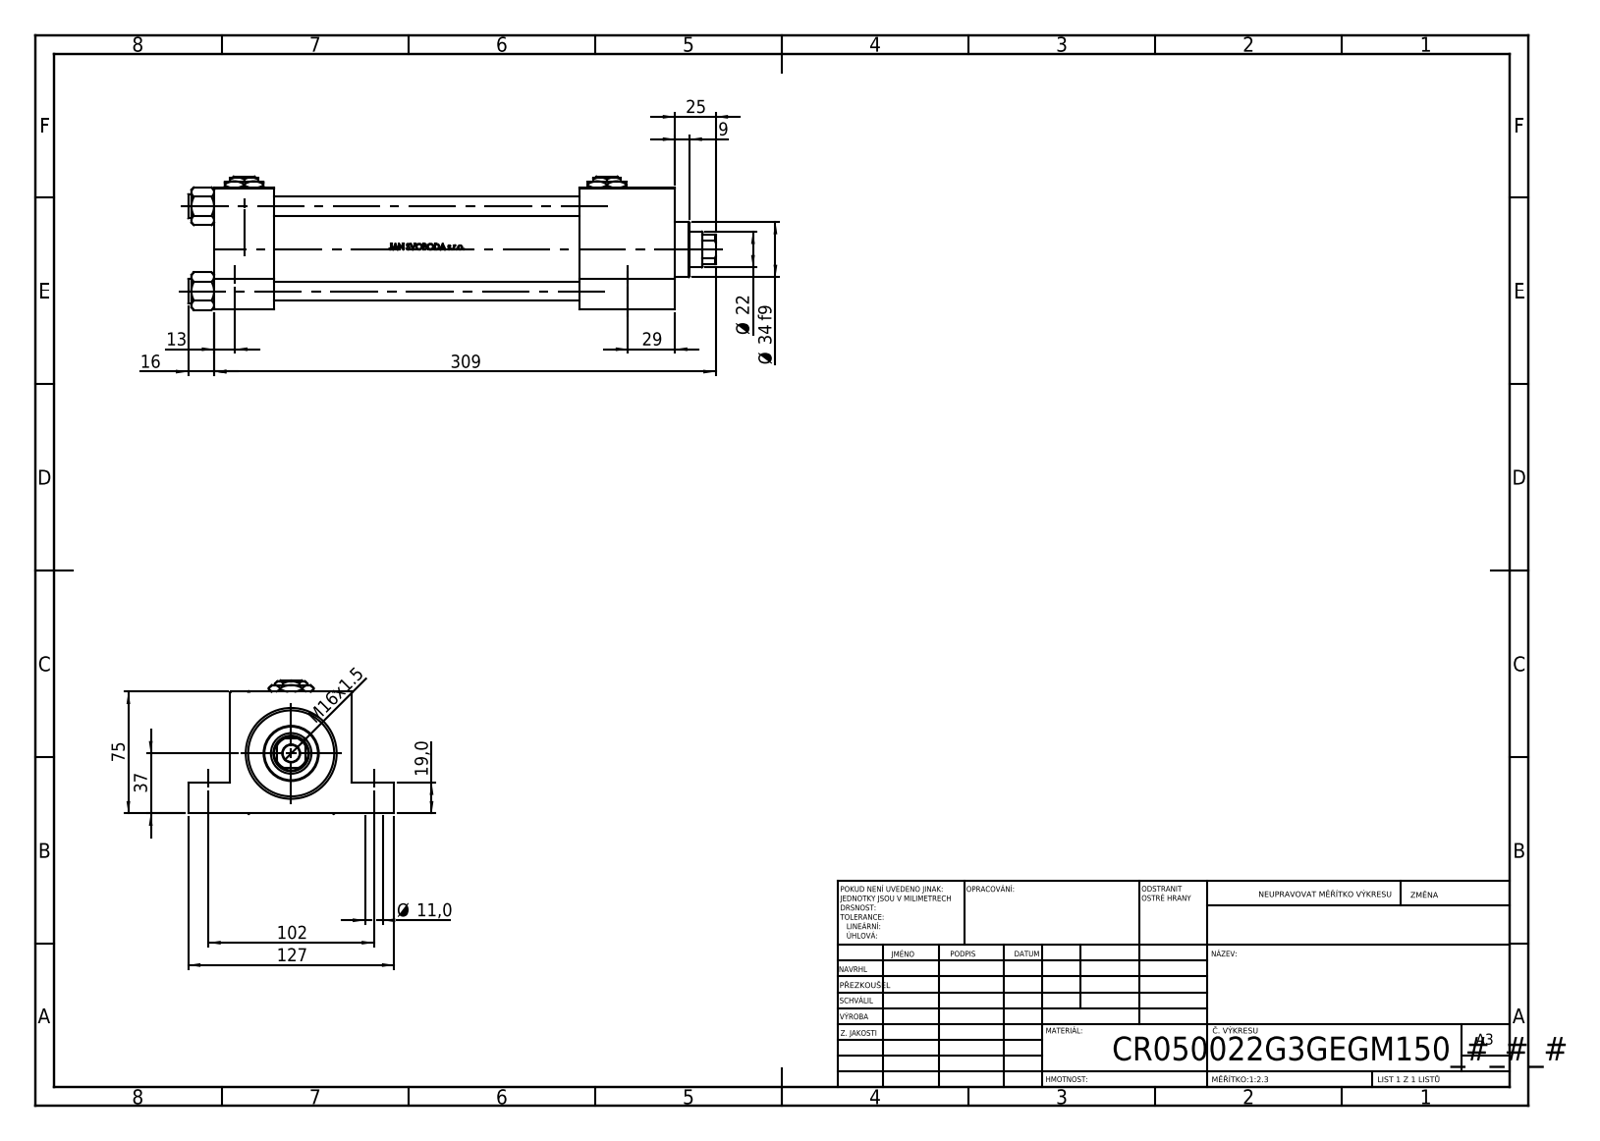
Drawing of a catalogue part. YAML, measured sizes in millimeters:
part_name: "NUT_M5_G; V215_VC_A; V215CR_G_Body; V215CR_G_TYCINKA (+2 more)"
step_written_by: "SolidWorks 2019 (CONFIG_CONTROL_DESIGN)"
units: millimeters
bodies: {solids: 13, faces: 1172, planar: 476, cylindrical: 124, other: 572}
overall_size: [325, 127, 82.27]
volume: 934388
surface_area: 234172
round_holes:
  - {diameter: 11, count: 4}
  - {diameter: 12, count: 4}
  - {diameter: 7, count: 2}
  - {diameter: 20.96, count: 2}
  - {diameter: 30, count: 2}
  - {diameter: 10.5, count: 1}
  - {diameter: 22, count: 1}
  - {diameter: 25, count: 1}
  - {diameter: 41, count: 1}
  - {diameter: 50, count: 1}
  - {diameter: 53, count: 1}
round_bosses_or_shafts:
  - {diameter: 15, count: 4}
  - {diameter: 56, count: 1}
  - {diameter: 34, count: 1}
partial_cylinders:
  - {radius: 10.5, count: 1}
face_to_face_distances: [75, 37, 284, 247, 19, 56, 225, 188, 59, 26]
hole_center_spacings: [52.3, 36.63, 37.34, 51.3, 52.63, 73.96, 102, 234.61]
